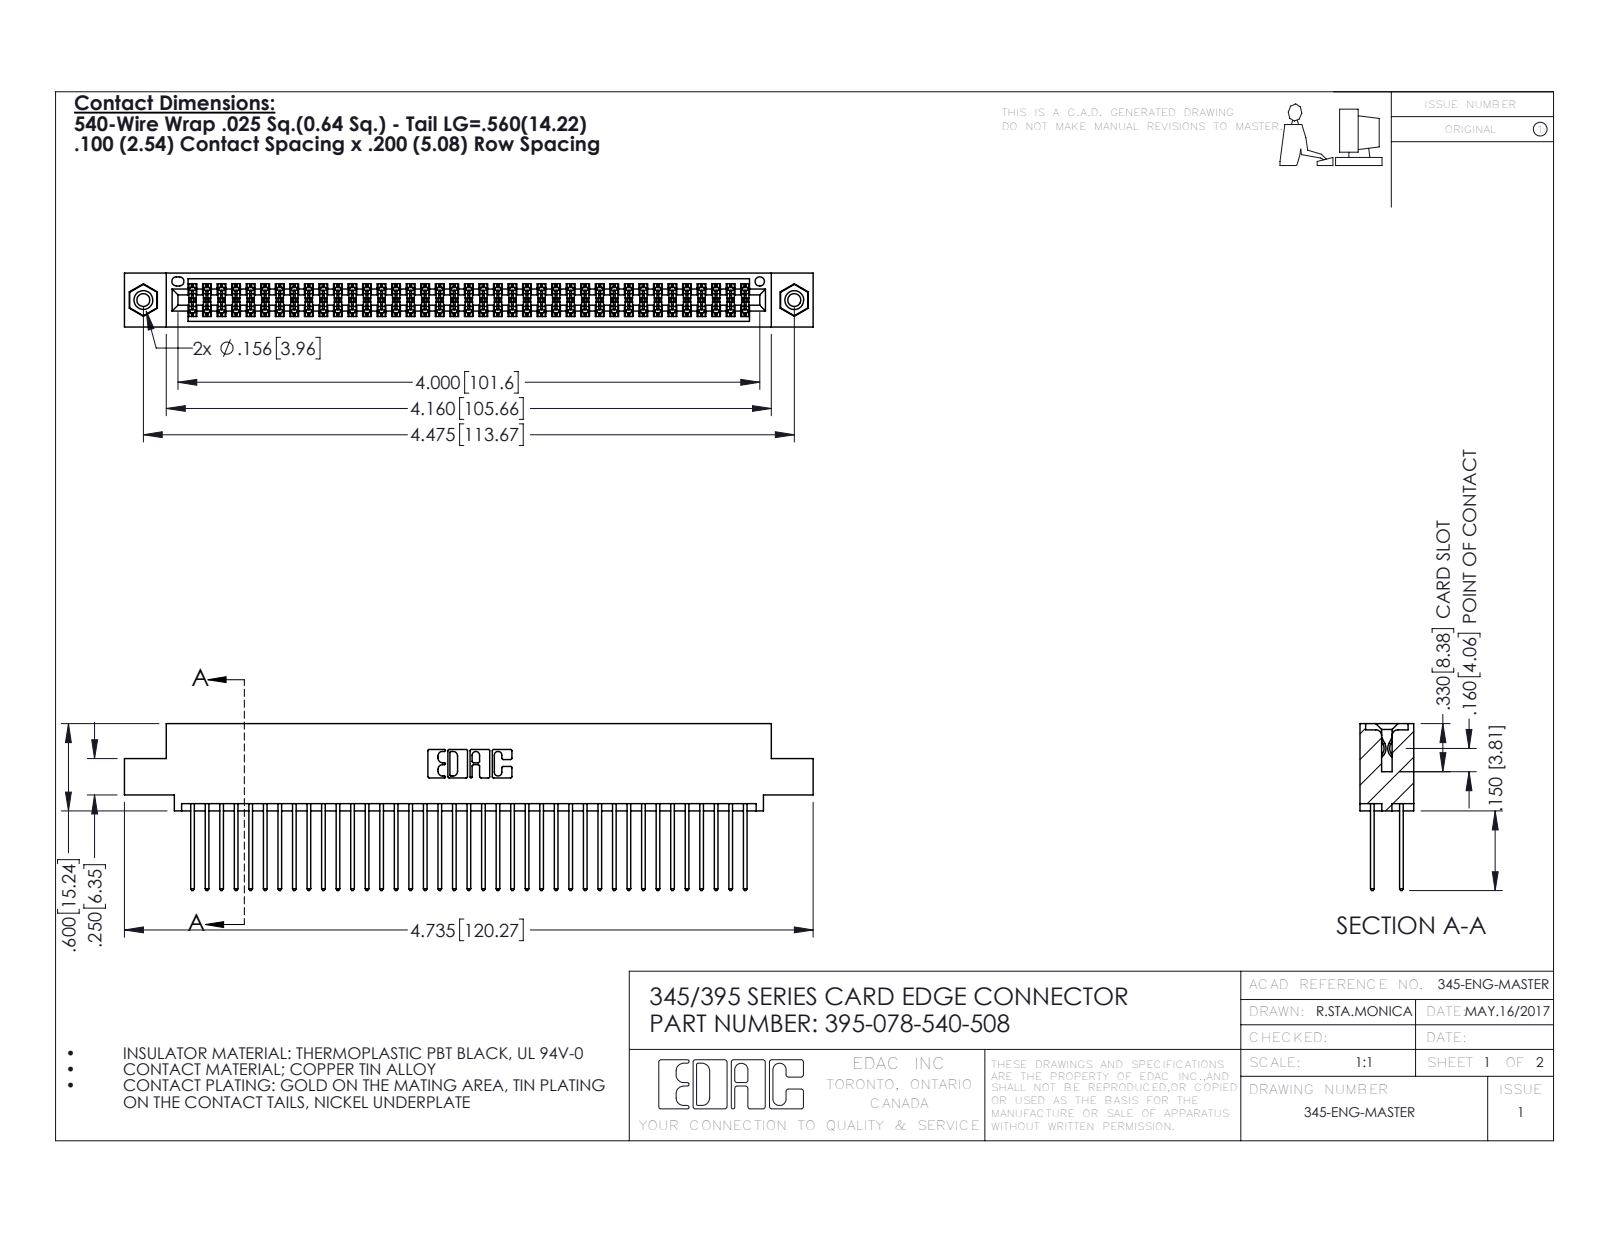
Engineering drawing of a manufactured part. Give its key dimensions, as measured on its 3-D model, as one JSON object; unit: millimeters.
{"part_name": "345-292-001_345-293-140; 395-078-540-508; 345 Part_0.110 Offset - 0.156 Dia-TI; 345-250-001_345-250-003-102", "step_written_by": "SolidWorks 2016 (CONFIG_CONTROL_DESIGN)", "units": "millimeters", "bodies": {"solids": 81, "faces": 4090, "planar": 2690, "cylindrical": 1384, "other": 16}, "overall_size": [120.3, 29.1, 9.4], "volume_mm3": 11900, "surface_area_mm2": 18970, "round_holes": [[2.3, 2], [3.2, 2], [4, 2], [1.6, 1]], "round_bosses_or_shafts": [[3.9, 2]], "partial_cylinders_radius": [[0.2, 117], [0.3, 78], [0.3, 22], [0.2, 6], [0.8, 6], [0.7, 3], [0.4, 2], [0.5, 2]], "face_to_face_distances": [1.8, 7.6, 5.1, 2.5, 6.9, 0.6, 9.4, 5.7, 4.4, 3.8], "hole_center_spacings": [6.9, 107.7, 113.7]}
